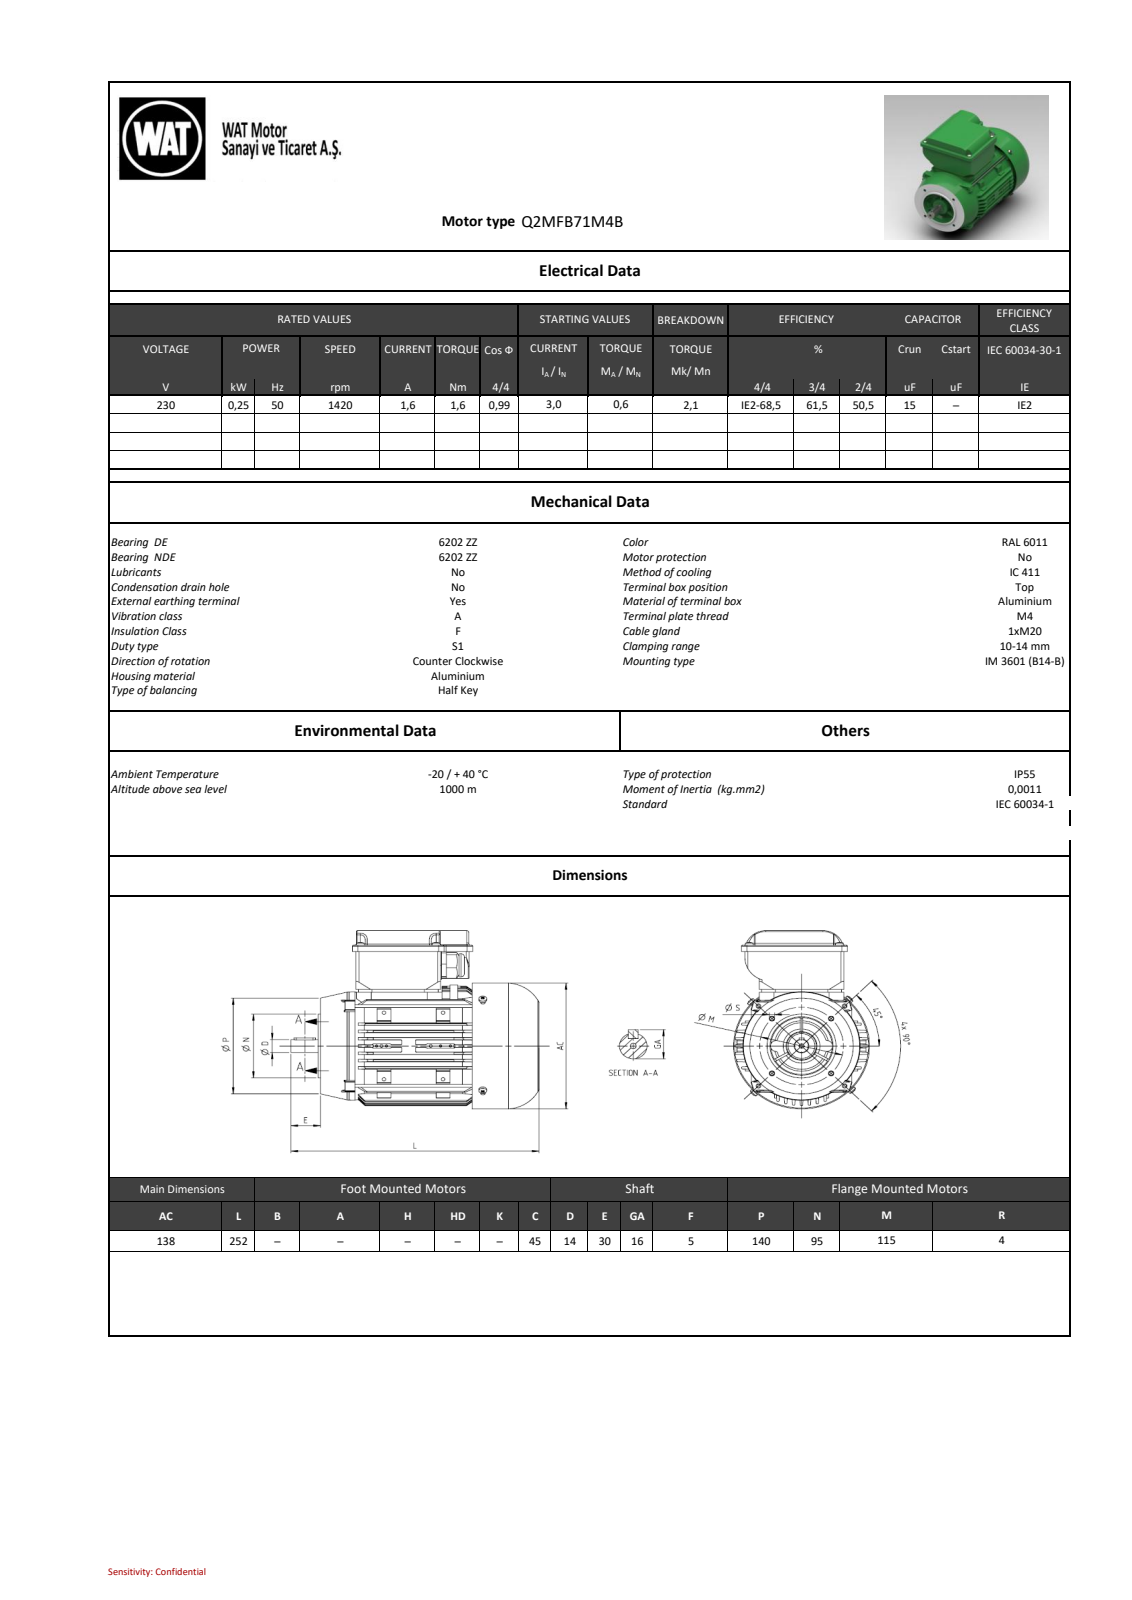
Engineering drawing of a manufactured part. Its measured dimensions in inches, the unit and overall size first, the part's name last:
Units: inches
Overall size (bounding box): 9.921 × 7.746 × 5.531
Round holes (diameter × count): ⌀0.13 ×9, ⌀0.144 ×8, ⌀0.177 ×8, ⌀0.098 ×6, ⌀0.315 ×5, ⌀0.157 ×4, ⌀0.183 ×4, ⌀0.189 ×4, ⌀0.118 ×3, ⌀0.146 ×3, ⌀0.181 ×2, ⌀0.197 ×1
Round bosses / shafts (diameter × count): ⌀0.315 ×8, ⌀0.157 ×8, ⌀0.118 ×8, ⌀0.13 ×4, ⌀5.531 ×1, ⌀5.433 ×1, ⌀5.354 ×1, ⌀4.528 ×1
Partial cylindrical surfaces — rounded edges, fillets, slot ends (radius × count): R0.039 ×89, R0.079 ×77, R0.047 ×36, R0.02 ×32, R0.098 ×14, R0.217 ×13, R0.012 ×12, R0.059 ×12
Main face-to-face distances: 0.118, 7.303, 0.157, 0.272, 1.264, 1.378, 5.768, 2.539, 0.039, 0.138
Hole centre spacings: 3.326, 2.165, 1.441, 2.362, 0.172, 1.467, 2.264, 2.436
Volume: 46.32 in³ · Surface area: 734.3 in²
Bodies: 24 solids, 2554 faces (1237 planar, 683 cylindrical, 634 other)
Part name (STEP PRODUCT): BY6434017xx_004-TK_QM63-80; BY6424130xx_004-TKK_QM63-80; BY6422457xx_005-MOTOR_KAPAGI_QS71FB_ISLEME; 641304741_AZ-KAMA PARALEL A 5x5x22 St50 DIN6885 (+7 more)
STEP written by: SIEMENS PLM Software NX2206.8101 (AUTOMOTIVE_DESIGN)
